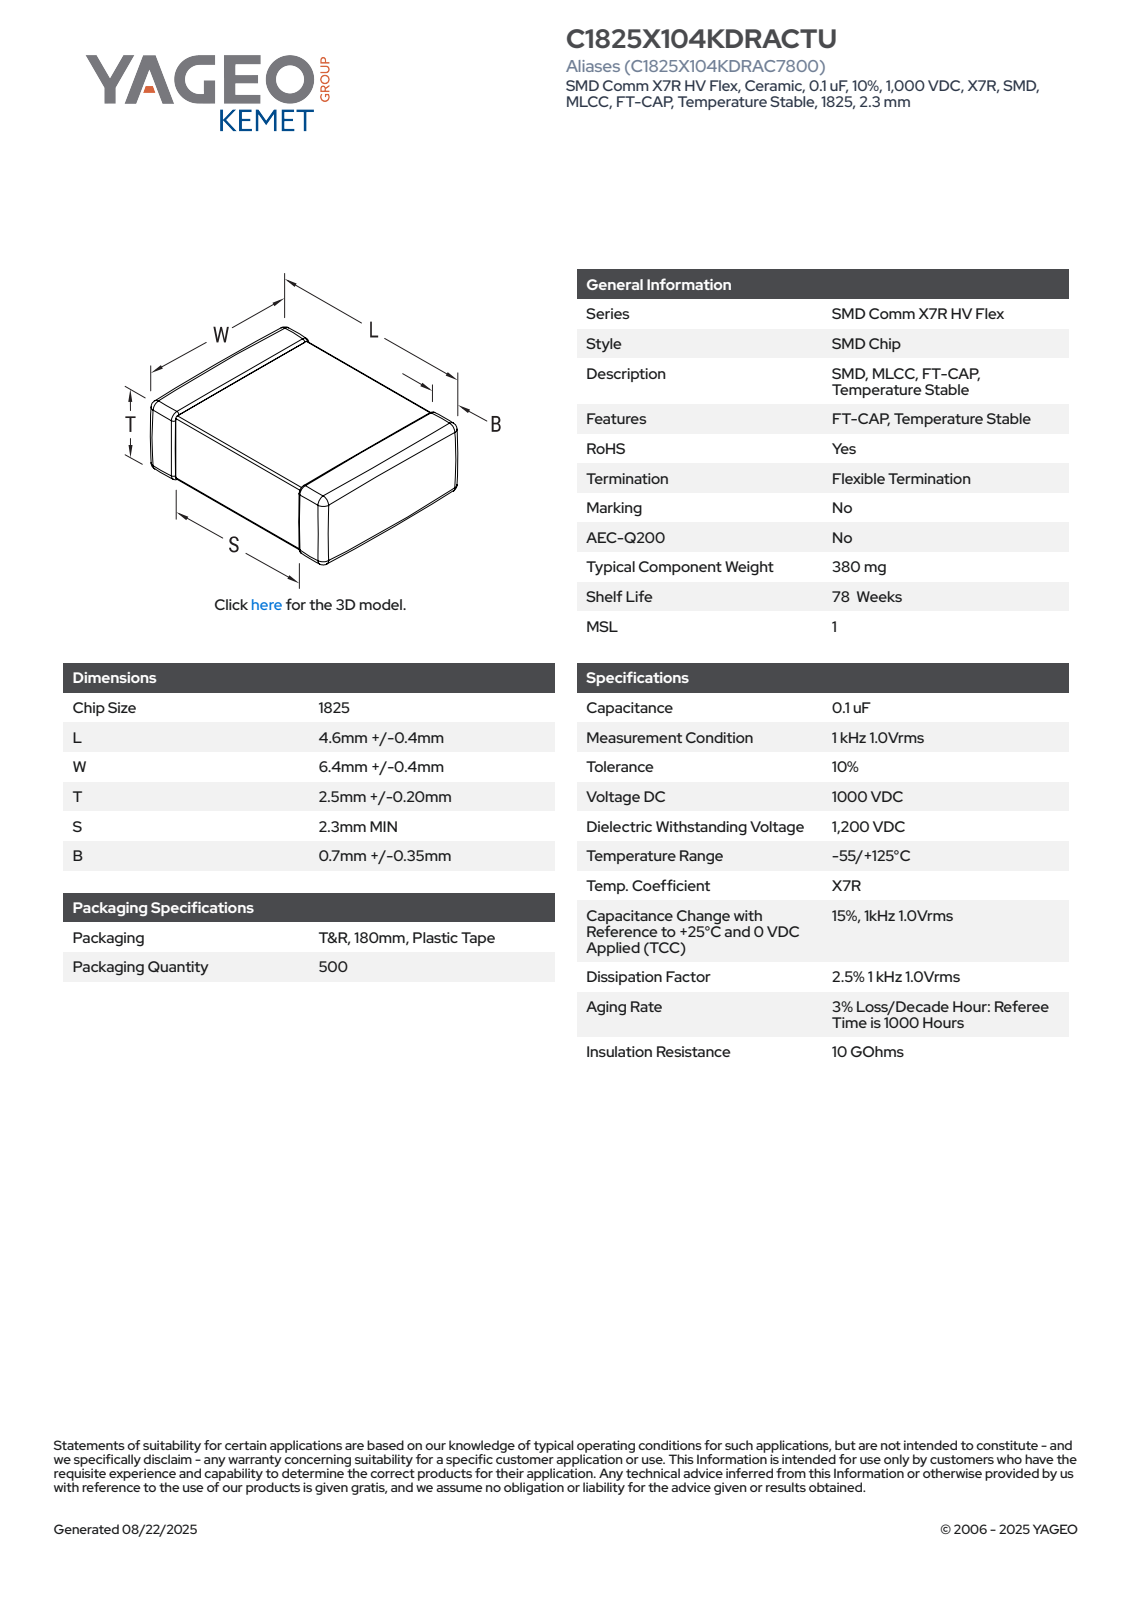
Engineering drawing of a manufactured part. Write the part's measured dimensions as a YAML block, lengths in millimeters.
part_name: "CCS_CCSTDNOS_1825_L5W6.8T2.7B1.05"
step_written_by: "SolidWorks 2014 (AUTOMOTIVE_DESIGN)"
units: millimeters
bodies: {solids: 4, faces: 121, planar: 71, cylindrical: 34, other: 16}
overall_size: [6.8, 5, 2.7]
volume: 84
surface_area: 129
partial_cylinders:
  - {radius: 0.14, count: 24}
face_to_face_distances: [2.56, 2.42, 5, 2.7, 6.66, 6.52, 6.8, 3.54, 3.12, 0.36]
